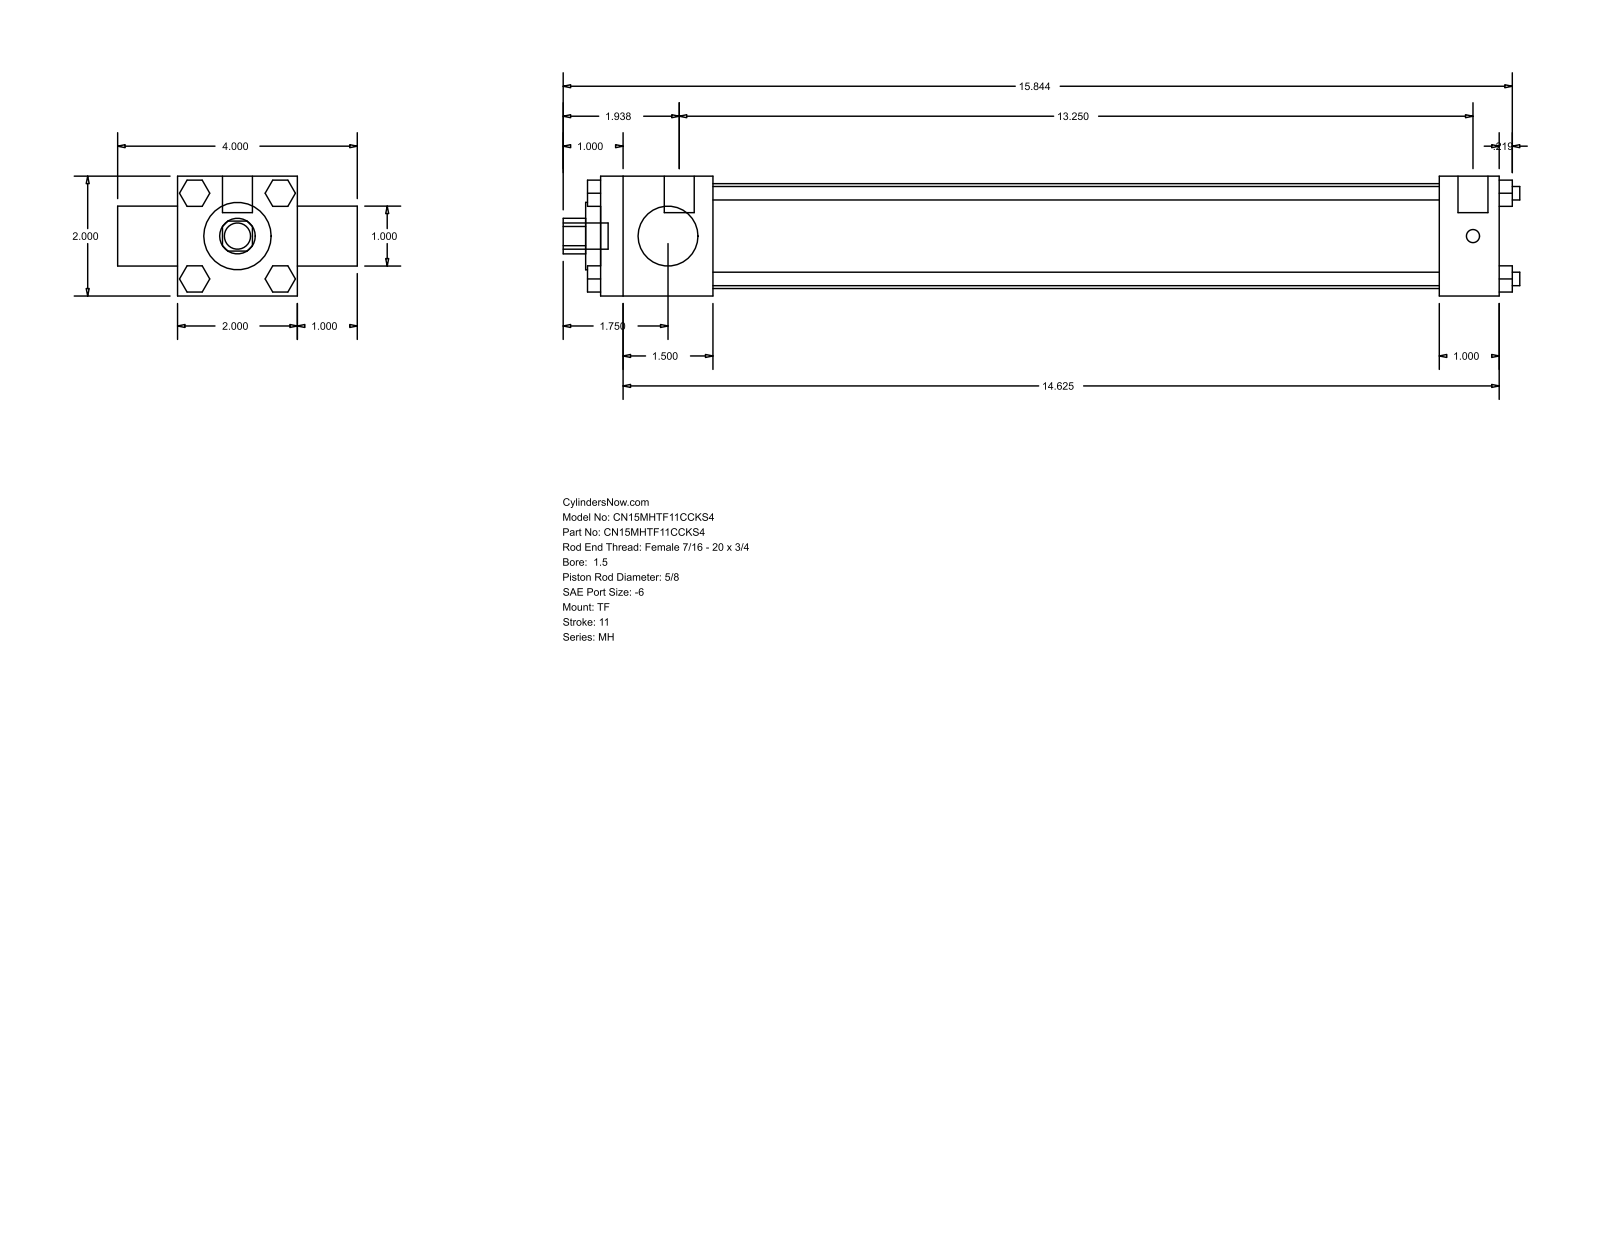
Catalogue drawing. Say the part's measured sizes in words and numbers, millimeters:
The part is named "MH_TF__0150_0.625". Its 3-D file was written by "GSSL Pune (CONFIG_CONTROL_DESIGN)". It is 0 solids with 120 faces: 92 planar, 28 cylindrical and 0 other. Overall it measures 405.61 by 101.6 by 50.8 millimeters. Round holes: 1 of diameter 15.88, 1 of diameter 25.4, 1 of diameter 28.57, 1 of diameter 44.45. Round bosses or shafts: 4 of diameter 5.71, 3 of diameter 5.56, 2 of diameter 12.7, 1 of diameter 11.11. Partial cylindrical surfaces (rounded edges, fillets, slot ends): 1 of radius 7.54. The main face-to-face distances are 50.8, 25.4, 381, 76.2, 47.62, 333.38, 355.6, 307.98, 11.11, 18.16.
